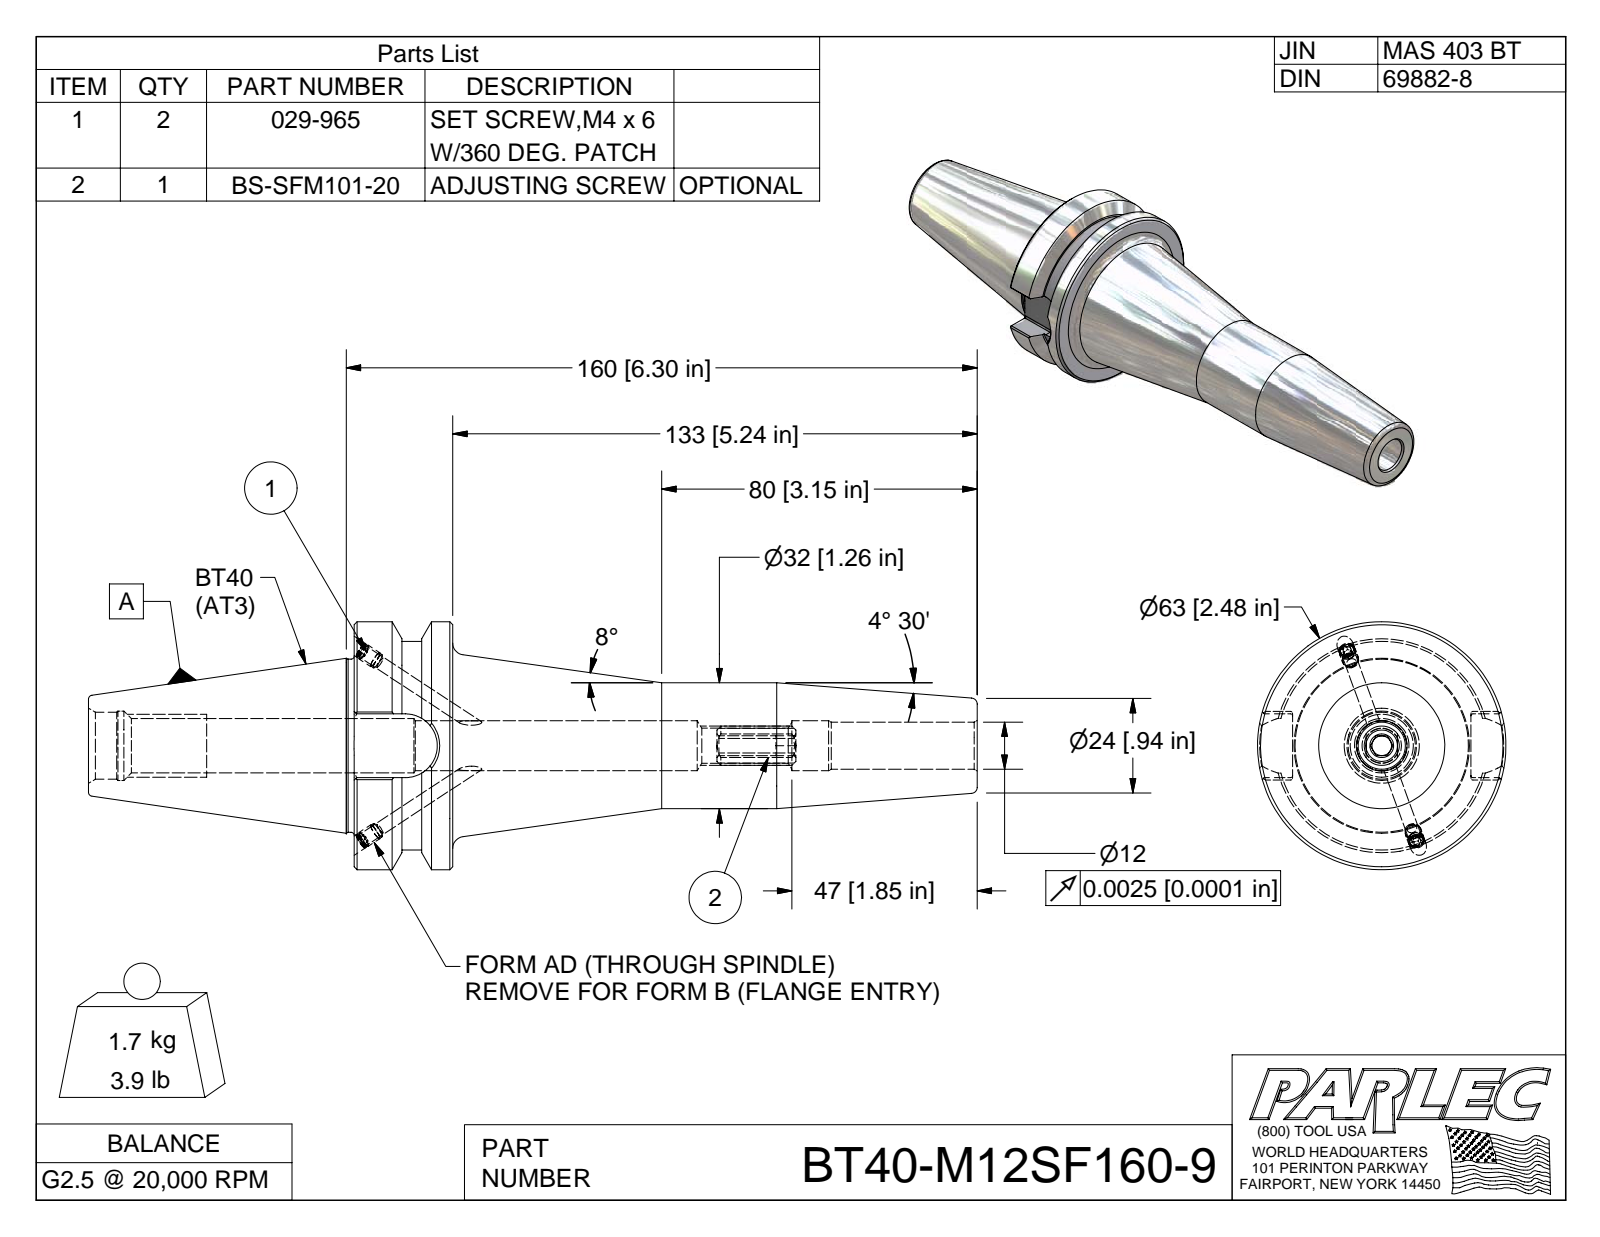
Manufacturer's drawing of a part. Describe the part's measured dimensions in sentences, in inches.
The part is named "BT40-M12SF160-9; BT40BC-M12SF160-9-1; 029-965; BS-SFM101-20". Its 3-D file was written by "Autodesk Inventor 2009 (AUTOMOTIVE_DESIGN)". It is 4 solids with 134 faces: 57 planar, 33 cylindrical and 44 other. Overall it measures 8.874 by 2.48 by 2.48 inches. Its volume is 13.79 cubic inches and its surface area 64.86 square inches. Round holes: 2 of diameter 0.13, 2 of diameter 0.161, 1 of diameter 0.471, 1 of diameter 0.501, 1 of diameter 0.694. Round bosses or shafts: 2 of diameter 0.165, 2 of diameter 0.157, 1 of diameter 2.48, 1 of diameter 2.087, 1 of diameter 1.75, 1 of diameter 1.73, 1 of diameter 1.26. Partial cylindrical surfaces (rounded edges, fillets, slot ends): 8 of radius 0.02, 1 of radius 0.197, 1 of radius 0.319. The main face-to-face distances are 0.984, 1.78, 0.733, 1.048, 6.221, 5.237, 2.653, 3.637, 8.874, 0.637.
